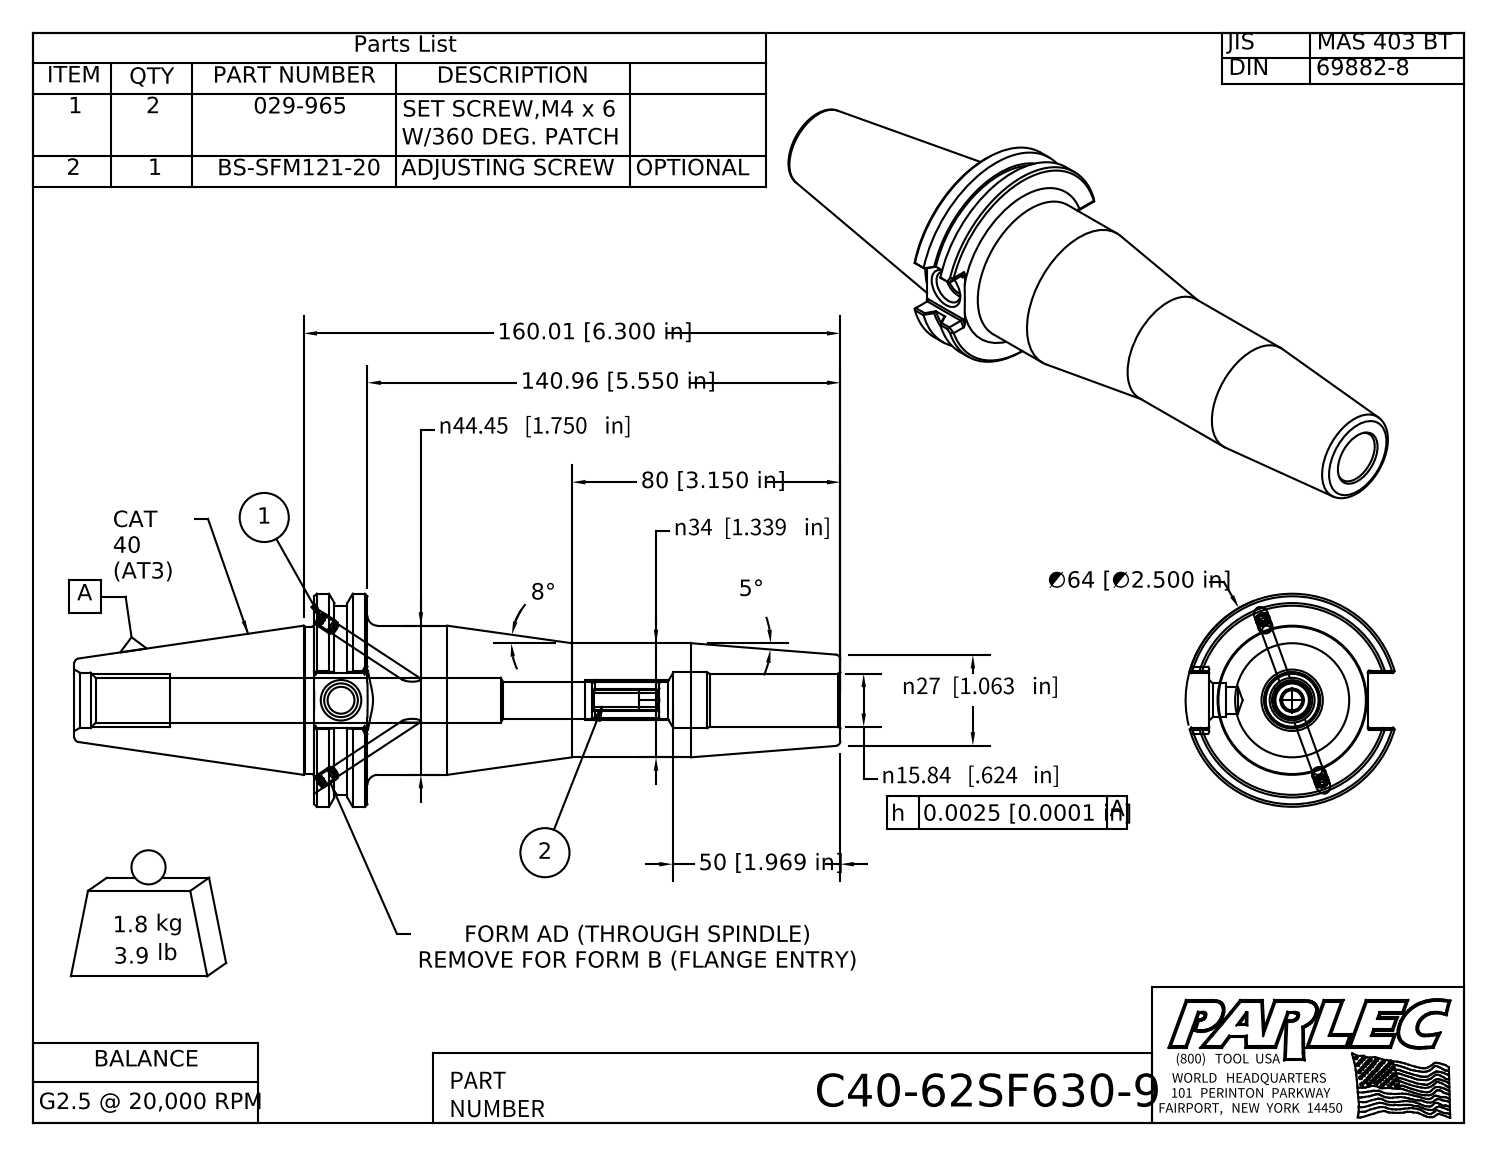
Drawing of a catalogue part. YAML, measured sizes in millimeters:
part_name: "C40-62SF630-9; C40BC-62SF630-9-1; 029-965; BS-SFM121-20"
step_written_by: "Autodesk Inventor 2009 (AUTOMOTIVE_DESIGN)"
units: millimeters
bodies: {solids: 4, faces: 153, planar: 66, cylindrical: 35, other: 52}
overall_size: [228.3, 63.5, 61.1]
volume: 227900
surface_area: 43140
round_holes:
  - {diameter: 3.3, count: 2}
  - {diameter: 4.1, count: 2}
  - {diameter: 15.8, count: 1}
  - {diameter: 16.6, count: 1}
round_bosses_or_shafts:
  - {diameter: 4.2, count: 2}
  - {diameter: 4, count: 2}
  - {diameter: 63.5, count: 1}
  - {diameter: 56.4, count: 1}
  - {diameter: 44.5, count: 1}
  - {diameter: 43.9, count: 1}
  - {diameter: 34, count: 1}
partial_cylinders:
  - {radius: 0.5, count: 12}
  - {radius: 6, count: 1}
face_to_face_distances: [15.9, 156.8, 141, 6, 16.3, 10, 47.2, 17.6, 29.7, 27.6]
